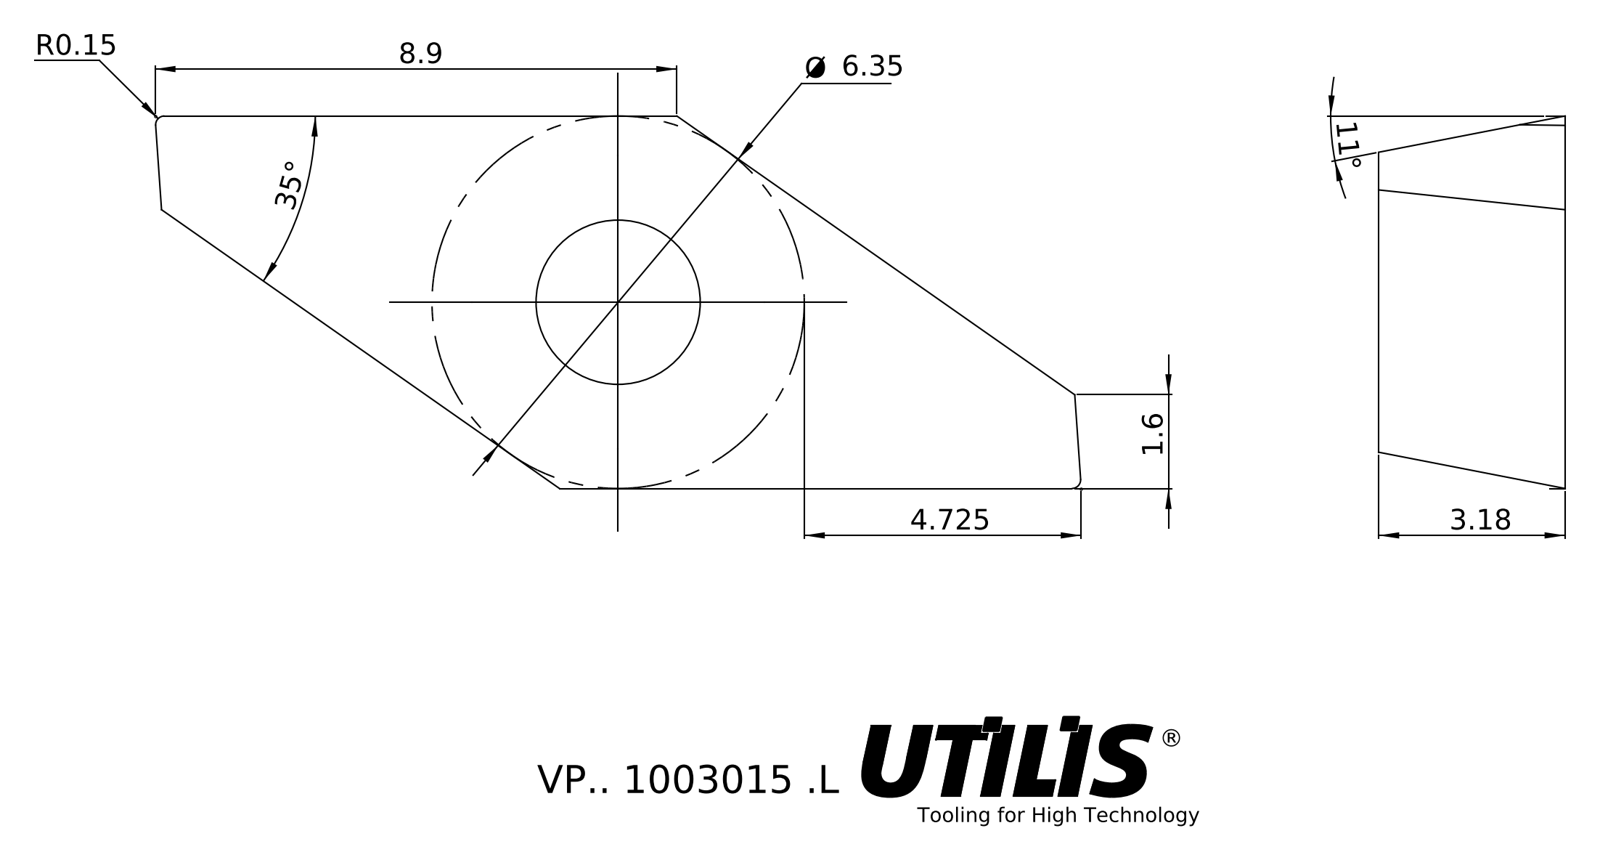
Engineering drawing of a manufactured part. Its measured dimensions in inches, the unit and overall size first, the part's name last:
Units: inches
Overall size (bounding box): 0.621 × 0.25 × 0.125
Round holes (diameter × count): ⌀0.11 ×1
Main face-to-face distances: 0.125
Volume: 0.01 in³ · Surface area: 0.375 in²
Bodies: 1 solid, 13 faces (8 planar, 2 cylindrical, 3 other)
Part name (STEP PRODUCT): VP.. 1003015 .L
STEP written by: SolidWorks 2016 (AUTOMOTIVE_DESIGN)
